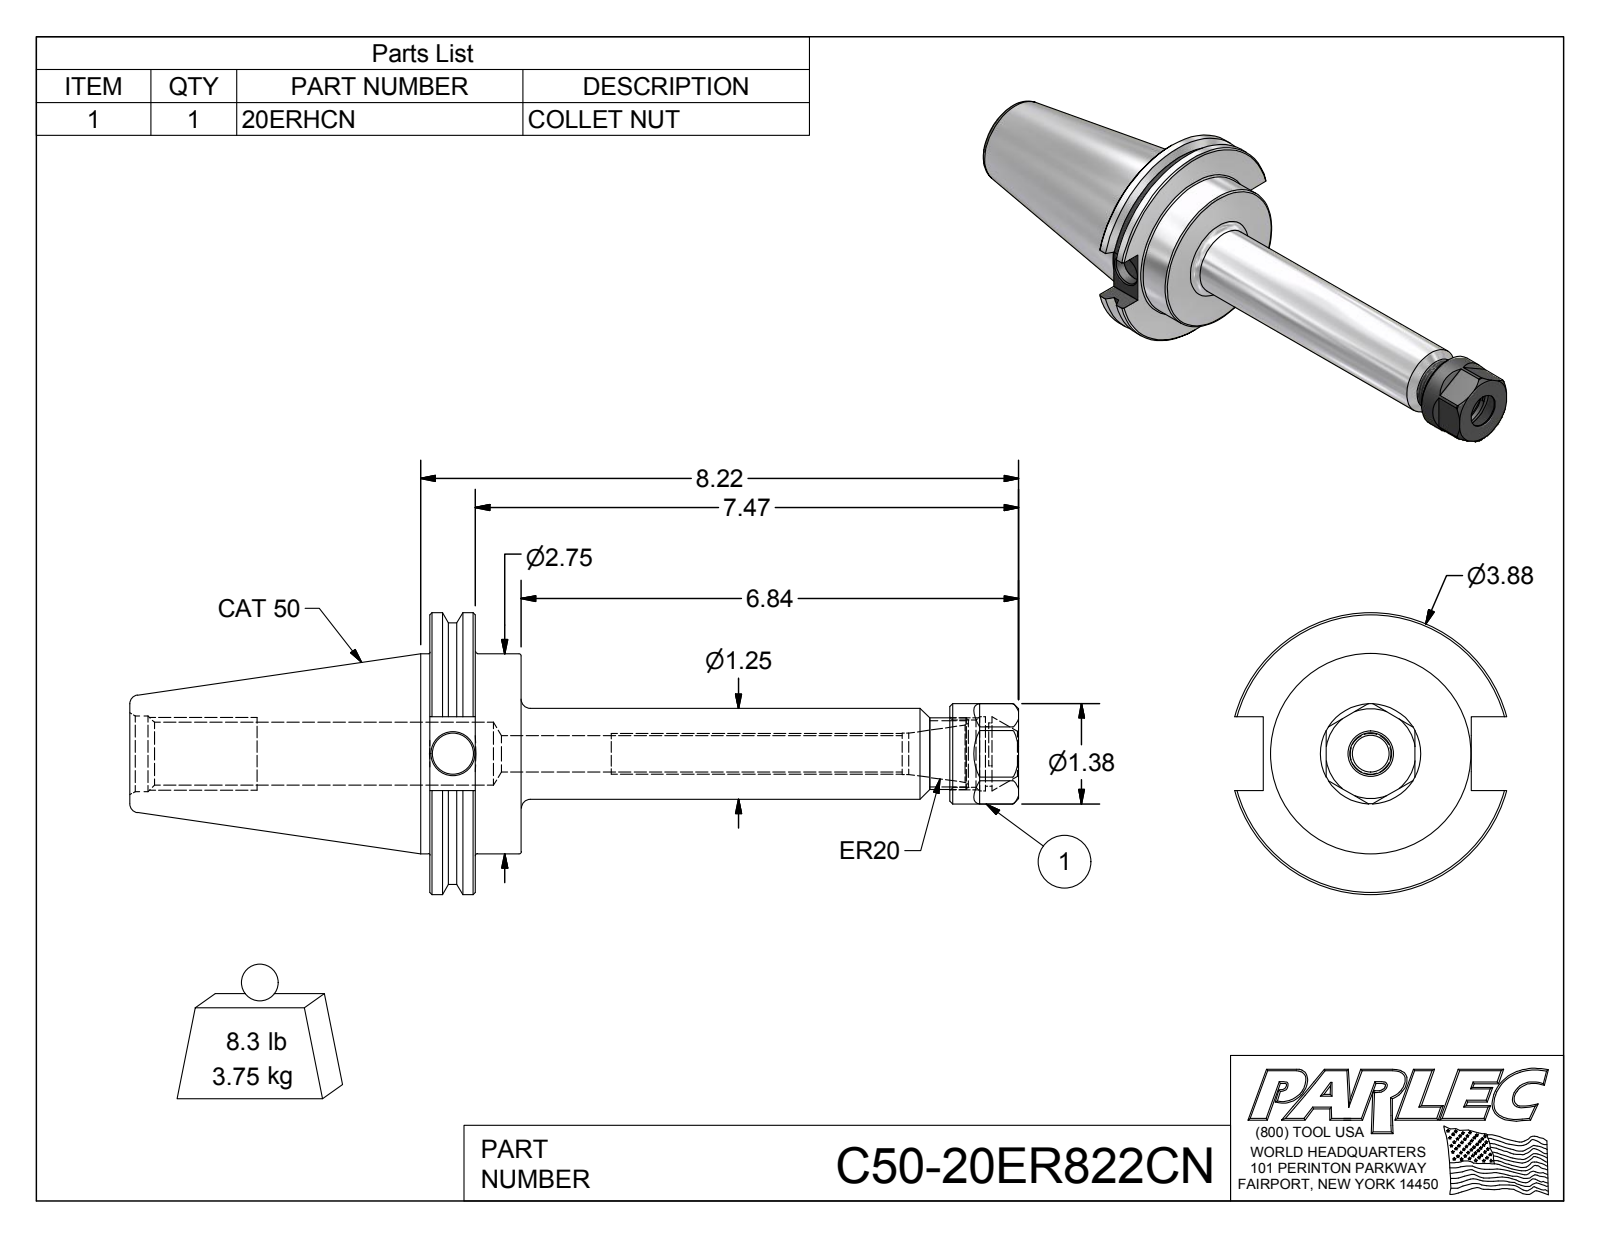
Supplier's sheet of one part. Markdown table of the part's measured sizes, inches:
| quantity | value |
| --- | --- |
| part name | C50-20ER822CN; C50-20ER8-1; 20ERHCN |
| STEP written by | Autodesk Inventor 2012 (AUTOMOTIVE_DESIGN) |
| units | inches |
| bodies | 2 solids, 89 faces (29 planar, 21 cylindrical, 39 other) |
| overall size | 12.22 × 3.875 × 3.74 |
| volume | 29.49 in³ |
| surface area | 116.9 in² |
| round holes (diameter × count) | 0.502 × 1, 0.563 × 1, 0.57 × 1, 0.62 × 1, 0.82 × 1, 0.865 × 1, 0.925 × 1, 1.024 × 1, 1.038 × 1 |
| round bosses / shafts (diameter × count) | 3.875 × 1, 3.594 × 1, 2.75 × 1, 1.378 × 1, 1.25 × 1, 0.984 × 1 |
| partial cylindrical surfaces (radius × count) | 0.423 × 1 |
| main face-to-face distances | 0.625, 1.255, 0.63, 1.22, 8.095, 7.47, 6.84, 7.15, 6.525, 5.895 |
| hole center spacings | 0.037 |
